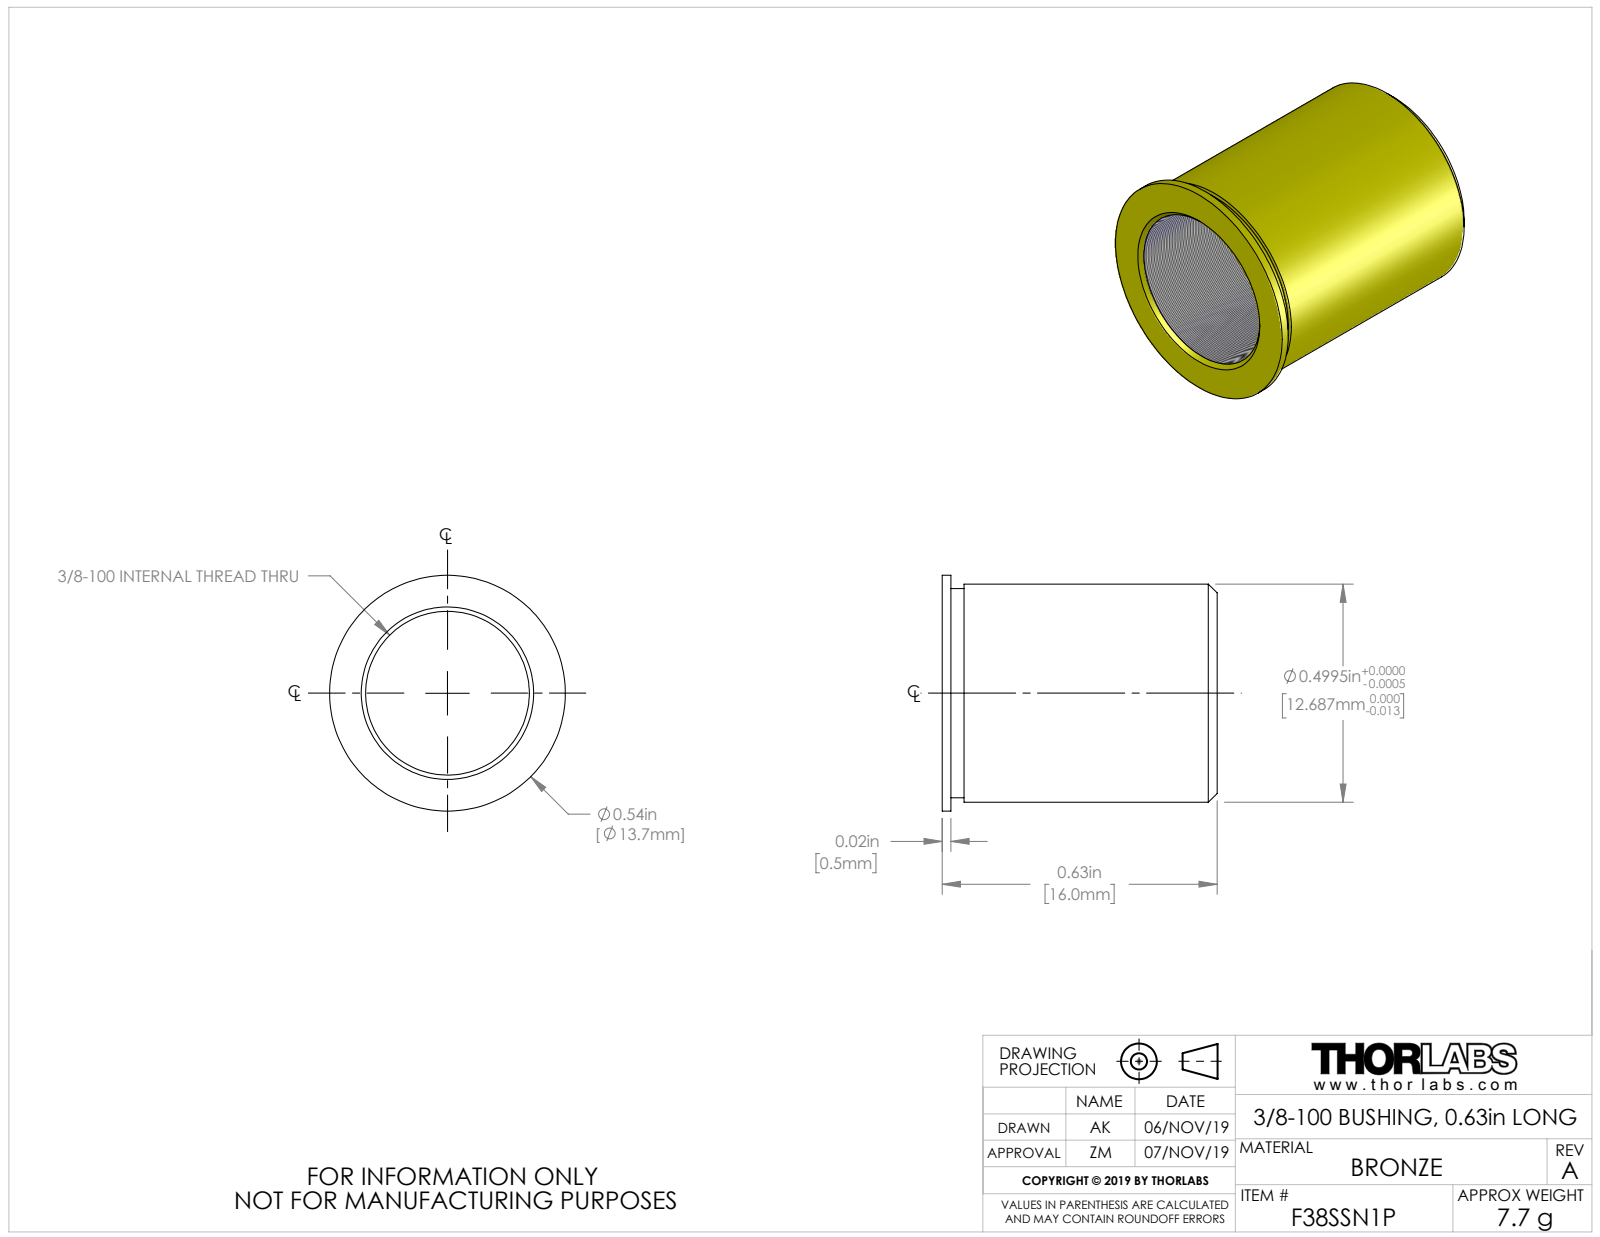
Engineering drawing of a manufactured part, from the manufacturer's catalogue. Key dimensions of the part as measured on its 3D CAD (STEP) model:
Part name (STEP PRODUCT): TTN200022-E0W
STEP written by: SolidWorks 2018 (AUTOMOTIVE_DESIGN)
Units: inches
Bodies: 1 solid, 18 faces (4 planar, 8 cylindrical, 6 other)
Overall size (bounding box): 0.63 × 0.54 × 0.54
Volume: 0.054 in³ · Surface area: 1.967 in²
Round holes (diameter × count): ⌀0.375 ×1
Round bosses / shafts (diameter × count): ⌀0.54 ×1, ⌀0.5 ×1, ⌀0.48 ×1
Main face-to-face distances: 0.02, 0.63, 0.61, 0.05, 0.03, 0.58
